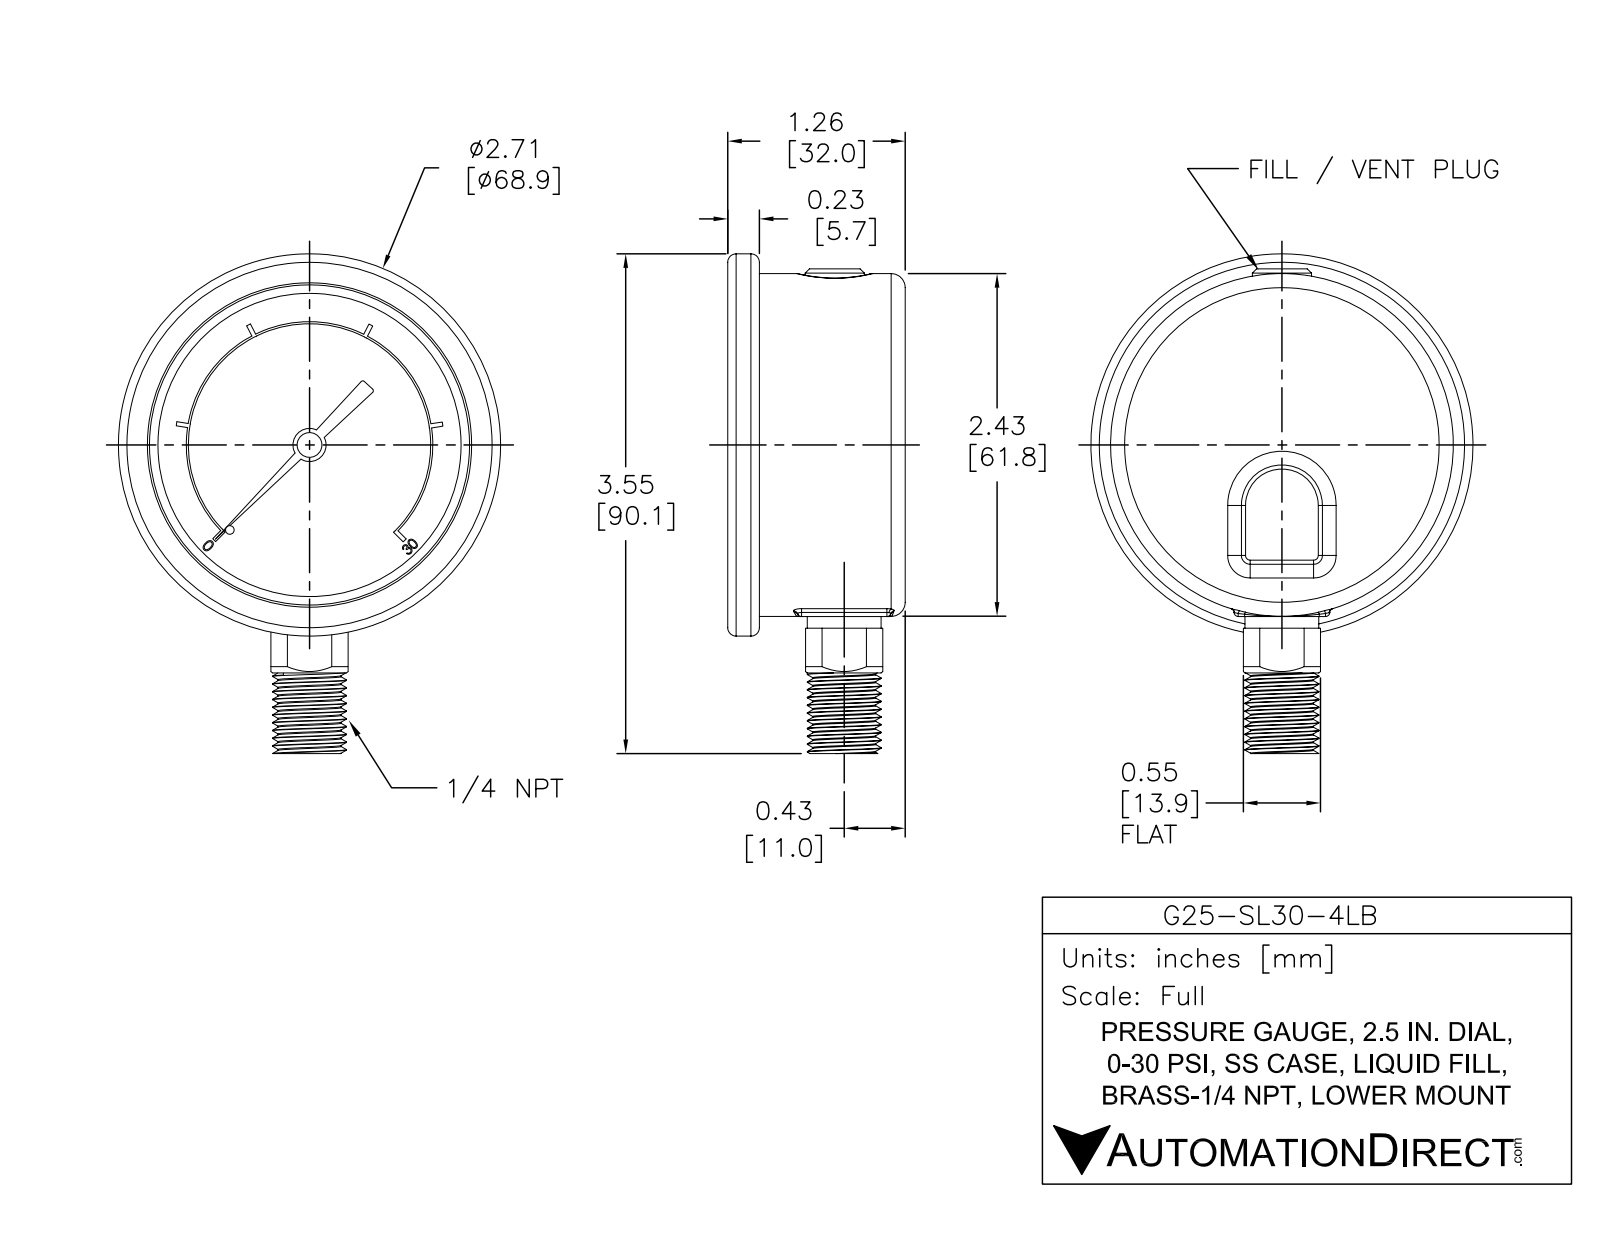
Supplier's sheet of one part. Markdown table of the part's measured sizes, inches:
| quantity | value |
| --- | --- |
| part name | G25-SL30-4LB |
| STEP written by | SolidWorks 2021 (AUTOMOTIVE_DESIGN) |
| units | inches |
| bodies | 1 solid, 343 faces (190 planar, 85 cylindrical, 68 other) |
| overall size | 3.546 × 2.713 × 1.26 |
| volume | 5.273 in³ |
| surface area | 24.68 in² |
| round holes (diameter × count) | 0.027 × 1, 0.071 × 1, 0.119 × 1, 2.272 × 1 |
| round bosses / shafts (diameter × count) | 2.713 × 1, 2.433 × 1, 0.524 × 1, 0.42 × 1, 0.235 × 1, 0.176 × 1, 0.14 × 1, 0.041 × 1 |
| partial cylindrical surfaces (radius × count) | 0.03 × 9, 0.1 × 3, 0.015 × 2, 0.316 × 1, 0.86 × 1, 0.875 × 1 |
| main face-to-face distances | 1.01, 1.26, 0.25, 1.035, 0.025, 0.225, 0.1, 0.91, 0.935, 1.16 |
| hole center spacings | 0.067 |
